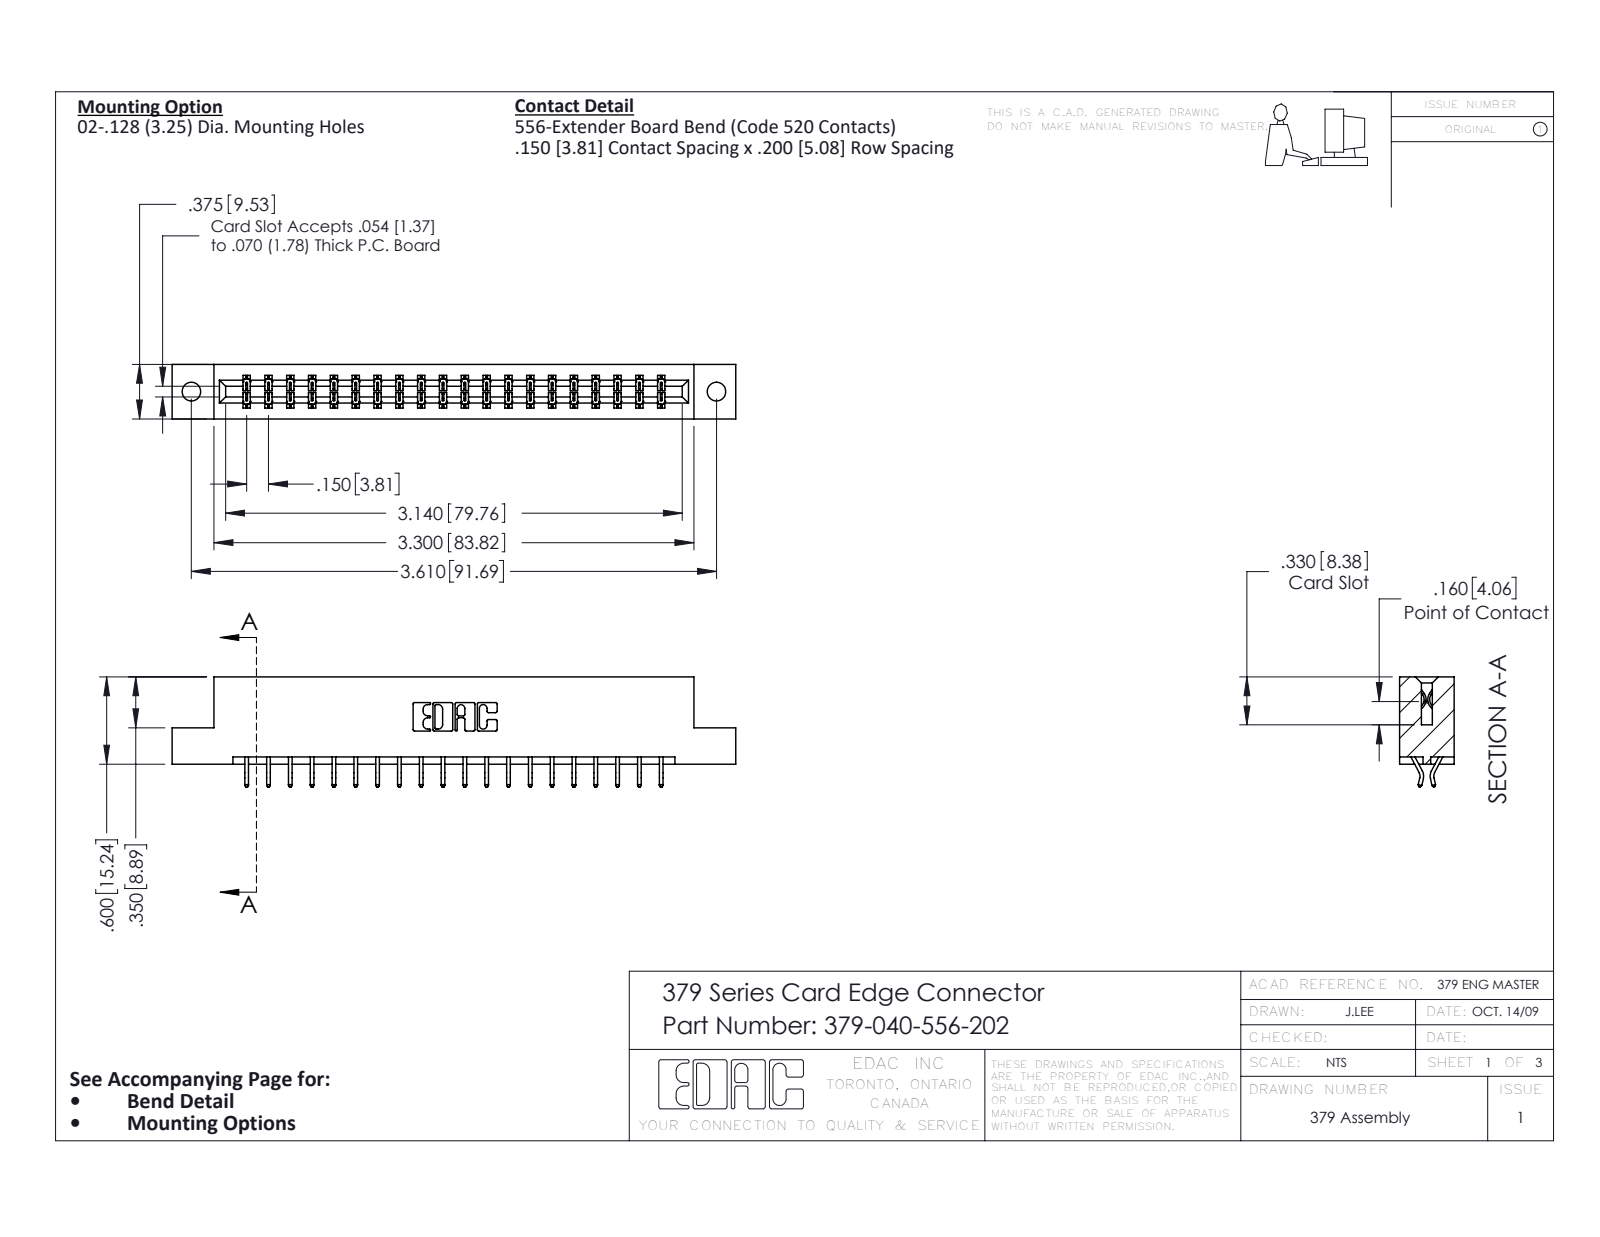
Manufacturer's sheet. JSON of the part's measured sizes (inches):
{"part_name": "379 Part_Flush - .128 Dia; 345-292-001_556 Tail; 379-040-556-202", "step_written_by": "SolidWorks 2016 (CONFIG_CONTROL_DESIGN)", "units": "inches", "bodies": {"solids": 41, "faces": 2434, "planar": 1670, "cylindrical": 764, "other": 0}, "overall_size": [3.875, 0.757, 0.375], "volume_in3": 0.621, "surface_area_in2": 16.91, "round_holes": [[0.128, 2]], "partial_cylinders_radius": [[0.006, 60], [0.01, 22], [0.007, 6], [0.031, 6], [0.026, 3], [0.01, 2], [0.014, 2], [0.022, 2]], "face_to_face_distances": [0.3, 0.075, 0.375, 0.2, 0.1, 0.225, 0.05, 0.15, 0.6, 0.55], "hole_center_spacings": [3.61]}
